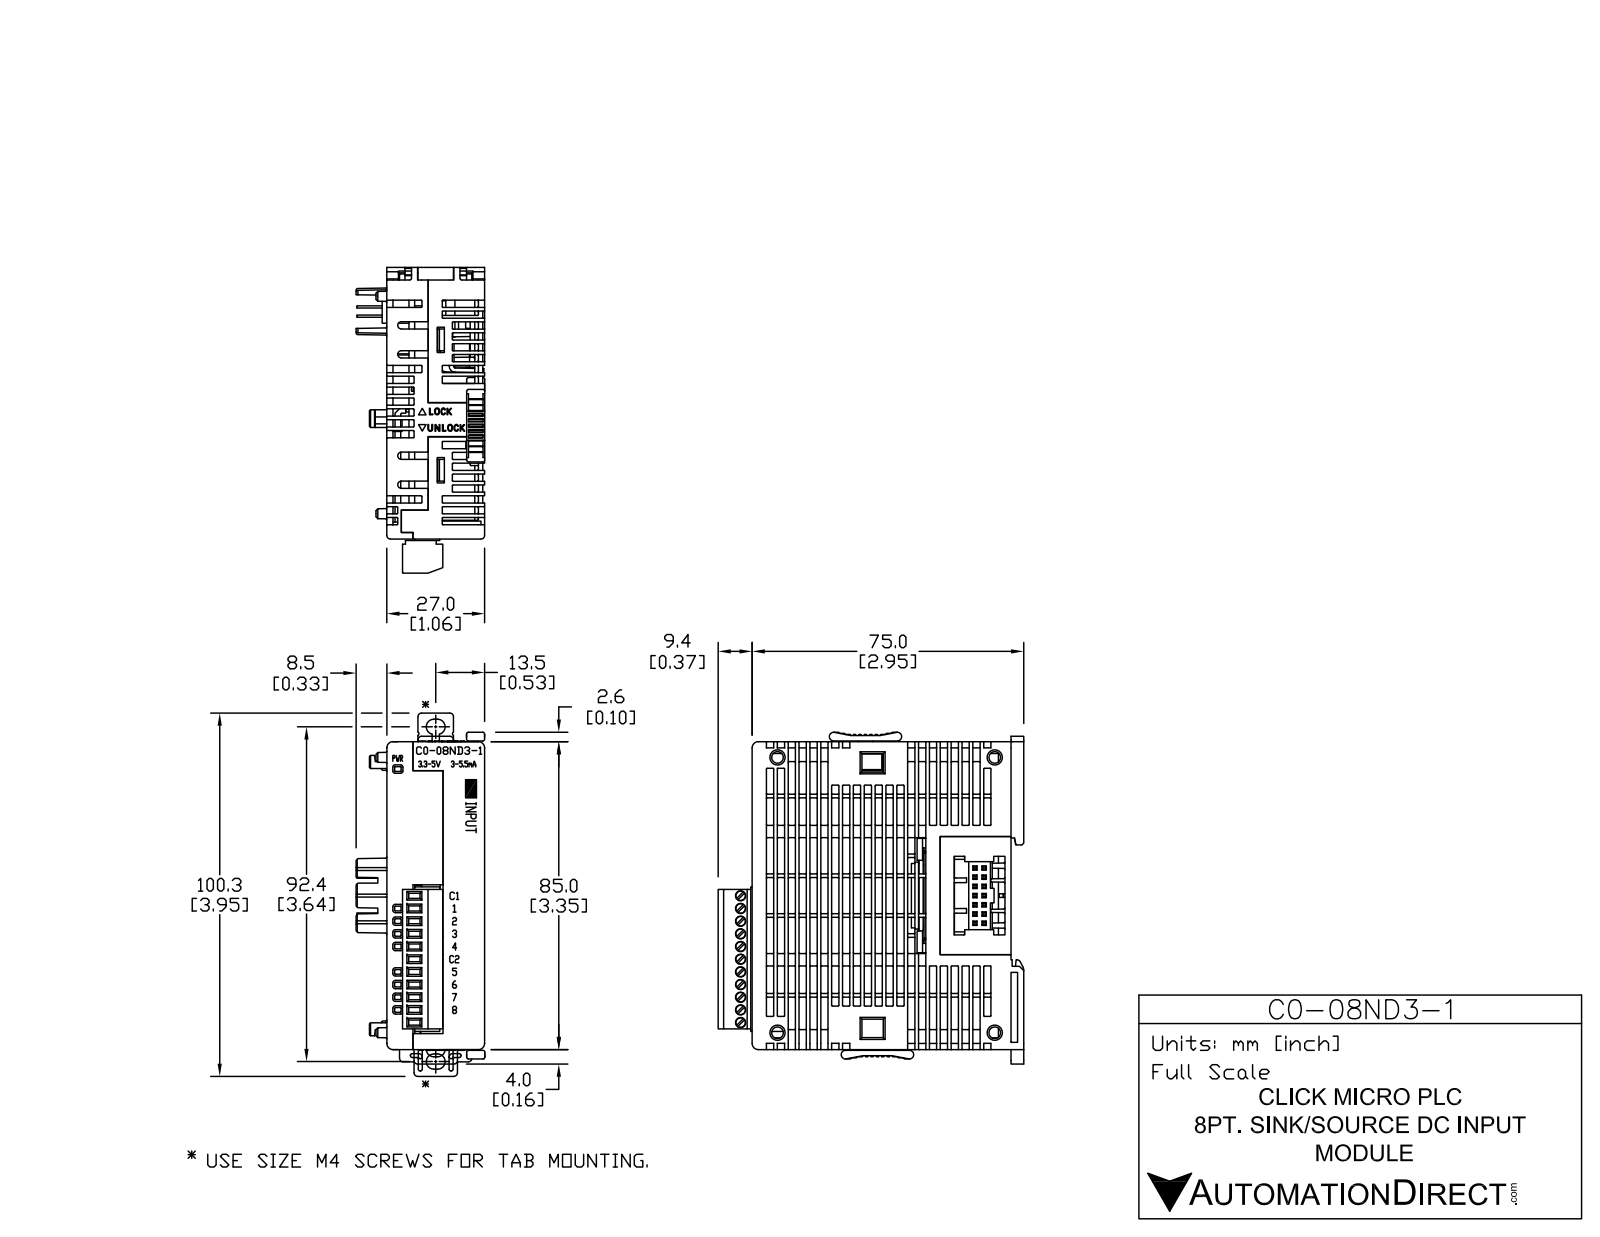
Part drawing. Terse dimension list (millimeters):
name: C0-08ND3-1
written by: SolidWorks 2009 (AUTOMOTIVE_DESIGN)
unit: mm
bodies: 1 solid, 3689 faces (2637 planar, 968 cylindrical, 84 other)
size: 91.6 × 84.4 × 35.55
volume: 162 505 mm³; area: 31 767 mm²
holes: 11× ⌀1, 11× ⌀2.8, 4× ⌀3.2, 2× ⌀2
bosses: 11× ⌀2.6, 1× ⌀1.9
rounds: 570× R0.2, 43× R0.5, 22× R0.3, 18× R1, 12× R1.2, 11× R2.8, 6× R1.7, 4× R2.1
face distances: 27.01, 0.5, 0.51, 26.5, 71.5, 1.7, 85, 26.3, 26.81, 84.5
hole spacings: 3.5, 7, 10.5, 14, 17.5, 21, 24.5, 28
